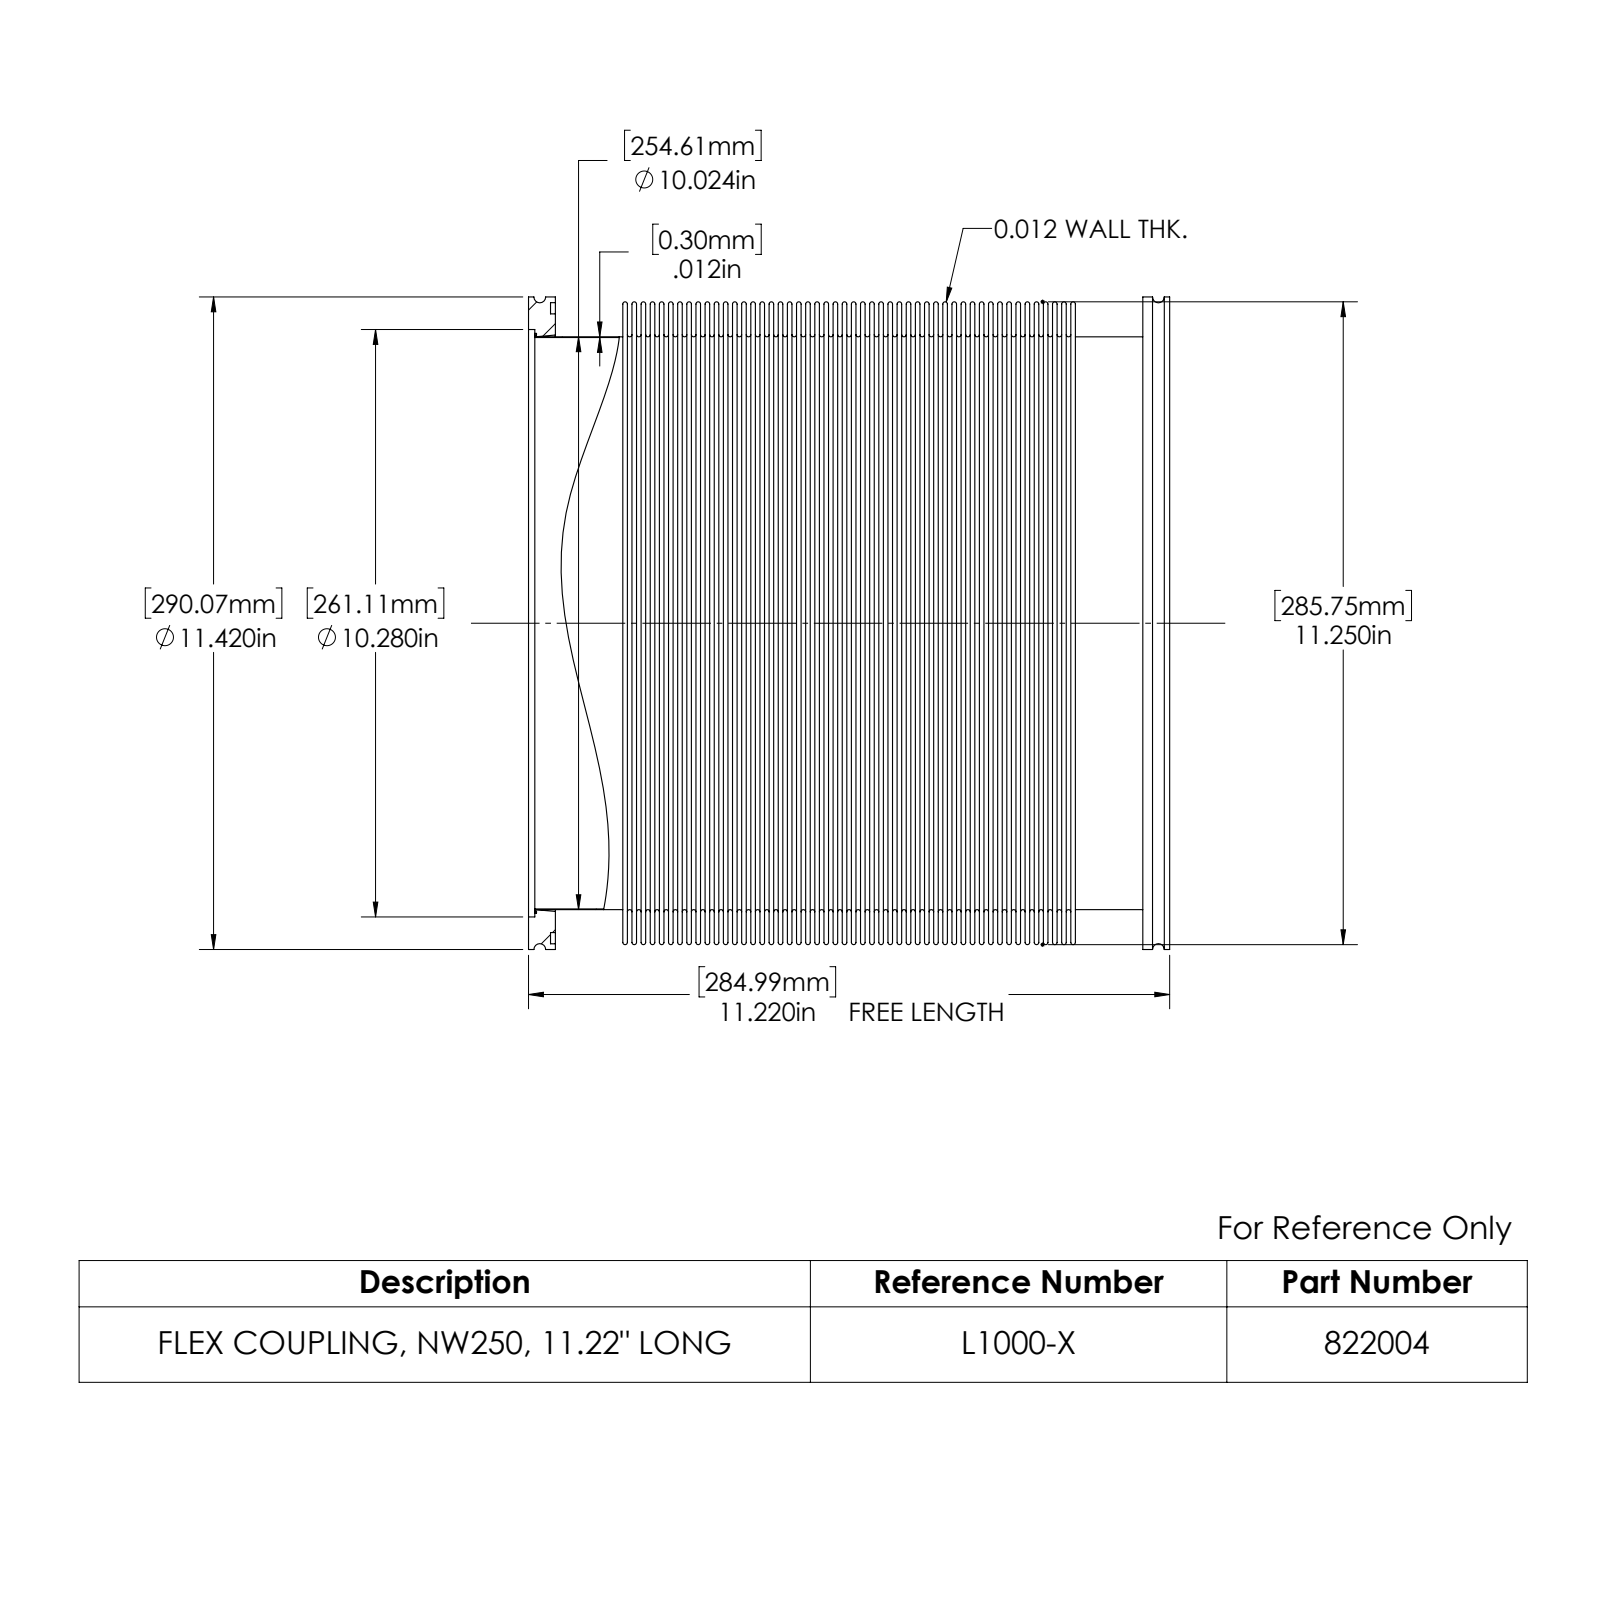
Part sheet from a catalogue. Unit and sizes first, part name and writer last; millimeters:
Units: millimetres
Overall size (bounding box): 290.1 × 290.1 × 285
Round holes (diameter × count): ⌀247.7 ×1, ⌀254 ×1, ⌀254.5 ×1, ⌀257.7 ×1, ⌀261.1 ×1, ⌀285 ×1
Round bosses / shafts (diameter × count): ⌀290.1 ×1, ⌀275 ×1, ⌀256.1 ×1, ⌀254.6 ×1
Main face-to-face distances: 8.1, 12.2, 20.3, 4.1, 28.4, 16.3, 24.4, 32.5, 4.1, 16.3
Volume: 766 600 mm³ · Surface area: 3 079 000 mm²
Bodies: 3 solids, 853 faces (215 planar, 36 cylindrical, 602 other)
Part name (STEP PRODUCT): 813004; 040611; 822004
STEP written by: SolidWorks 2022 (CONFIG_CONTROL_DESIGN)
